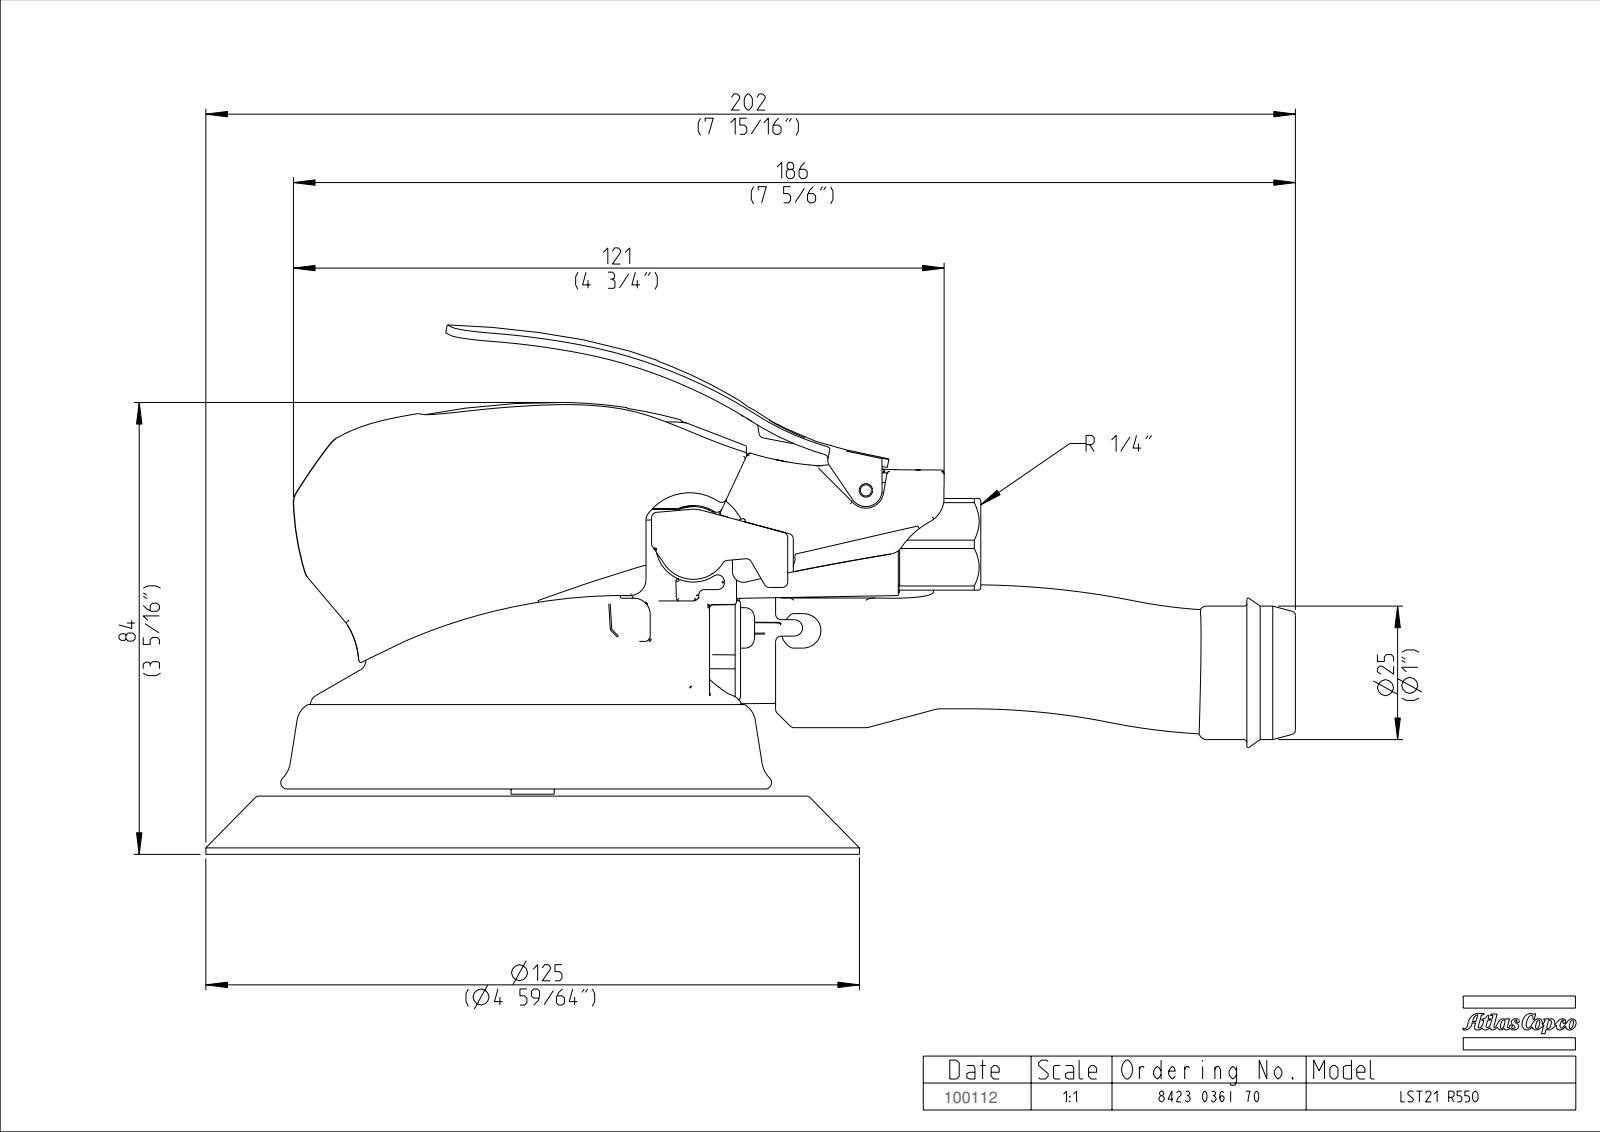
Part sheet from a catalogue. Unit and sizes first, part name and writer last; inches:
Units: inches
Overall size (bounding box): 7.954 × 4.772 × 3.865
Round holes (diameter × count): ⌀0.082 ×1, ⌀0.177 ×1
Round bosses / shafts (diameter × count): ⌀0.295 ×2, ⌀4.772 ×1, ⌀0.974 ×1, ⌀0.906 ×1, ⌀0.419 ×1, ⌀0.098 ×1
Partial cylindrical surfaces — rounded edges, fillets, slot ends (radius × count): R0.039 ×36, R0.02 ×30, R0.01 ×6, R0.012 ×6, R0.024 ×6, R0.059 ×6, R0.118 ×6, R0.197 ×4
Main face-to-face distances: 0.425, 1.093, 0.668, 2.545, 1.152, 3.696, 0.669, 0.354, 4.051, 2.899
Bodies: 0 solids, 715 faces (124 planar, 173 cylindrical, 418 other)
Part name (STEP PRODUCT): TMP95521_SW
STEP written by: PRO/ENGINEER BY PARAMETRIC TECHNOLOGY CORPORATION, 2008310 (CONFIG_CONTROL_DESIGN)
